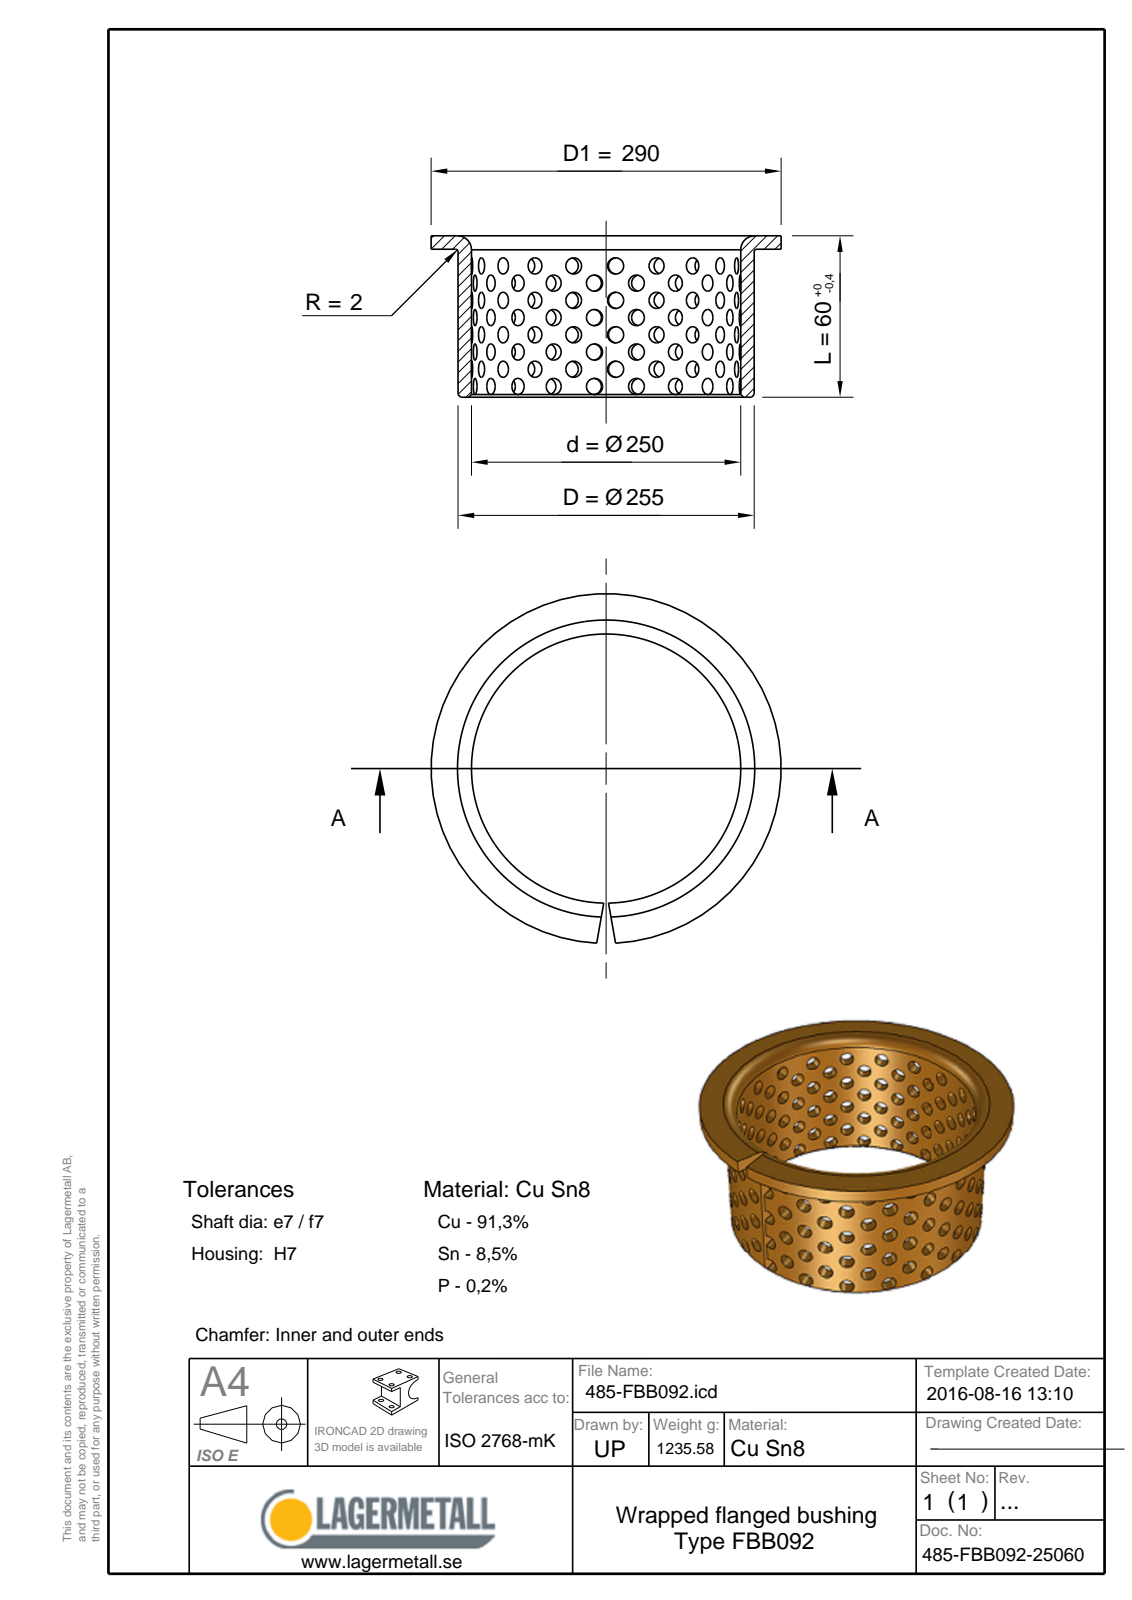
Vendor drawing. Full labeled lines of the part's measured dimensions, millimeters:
Part name (STEP PRODUCT): 485-FBB092-25060
STEP written by: Spatial InterOp 3D (CONFIG_CONTROL_DESIGN)
Units: millimetres
Bodies: 1 solid, 12 faces (5 planar, 3 cylindrical, 4 other)
Overall size (bounding box): 290 × 289.95 × 60
Volume: 152 541 mm³ · Surface area: 126 437 mm²
Round holes (diameter × count): ⌀250 ×1
Round bosses / shafts (diameter × count): ⌀290 ×1, ⌀255 ×1
Main face-to-face distances: 2.5, 57.5, 60
